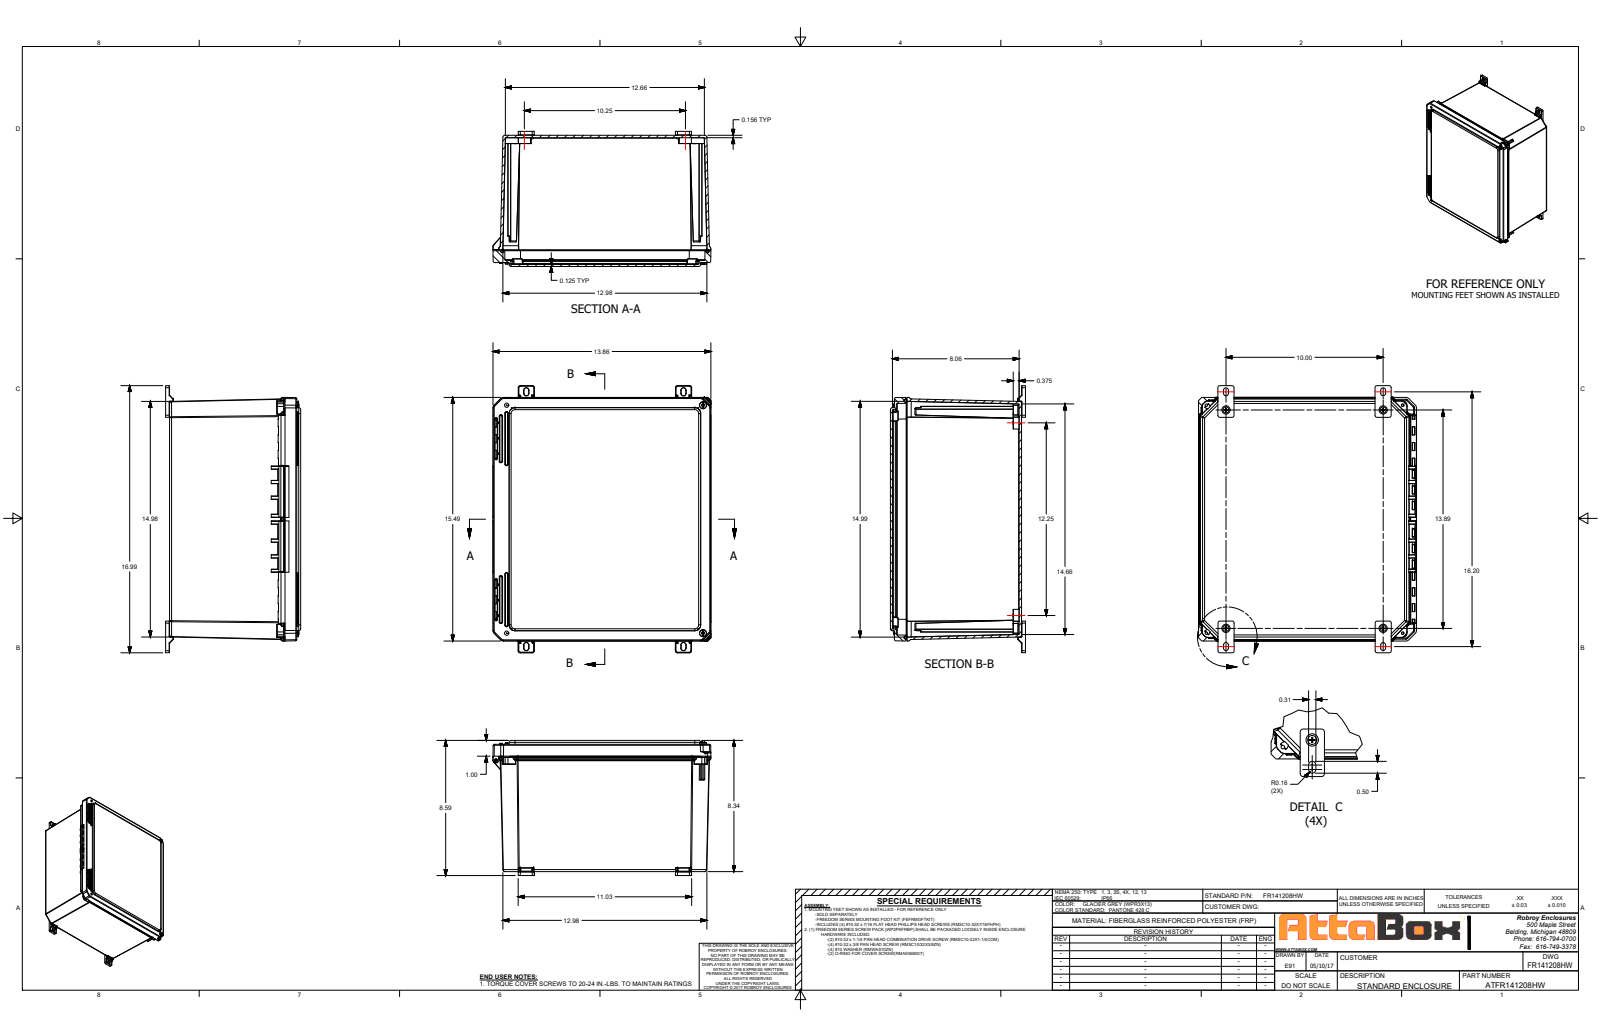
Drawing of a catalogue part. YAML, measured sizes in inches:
part_name: "FR141208HW"
step_written_by: "SolidWorks 2021 (AUTOMOTIVE_DESIGN)"
units: inches
bodies: {solids: 6, faces: 2154, planar: 670, cylindrical: 839, other: 645}
overall_size: [15.49, 13.864, 8.341]
volume: 144.2
surface_area: 1803
round_holes:
  - {diameter: 0.152, count: 8}
  - {diameter: 0.252, count: 4}
  - {diameter: 0.253, count: 4}
  - {diameter: 0.219, count: 2}
  - {diameter: 0.227, count: 2}
  - {diameter: 0.313, count: 2}
  - {diameter: 0.137, count: 1}
round_bosses_or_shafts:
  - {diameter: 0.45, count: 2}
  - {diameter: 0.435, count: 2}
  - {diameter: 0.199, count: 2}
  - {diameter: 0.135, count: 1}
partial_cylinders:
  - {radius: 0.01, count: 172}
  - {radius: 0.005, count: 88}
  - {radius: 0.02, count: 49}
  - {radius: 0.03, count: 45}
  - {radius: 0.03, count: 24}
  - {radius: 0.09, count: 24}
  - {radius: 0.096, count: 24}
  - {radius: 0.125, count: 22}
face_to_face_distances: [0.156, 0.125, 8.185, 8.341, 8.217, 8.061, 0.158, 0.16, 0.16, 0.159]
hole_center_spacings: [13.417, 13.835, 1.584, 11.248, 11.425, 14.489, 14.49, 17.551]
